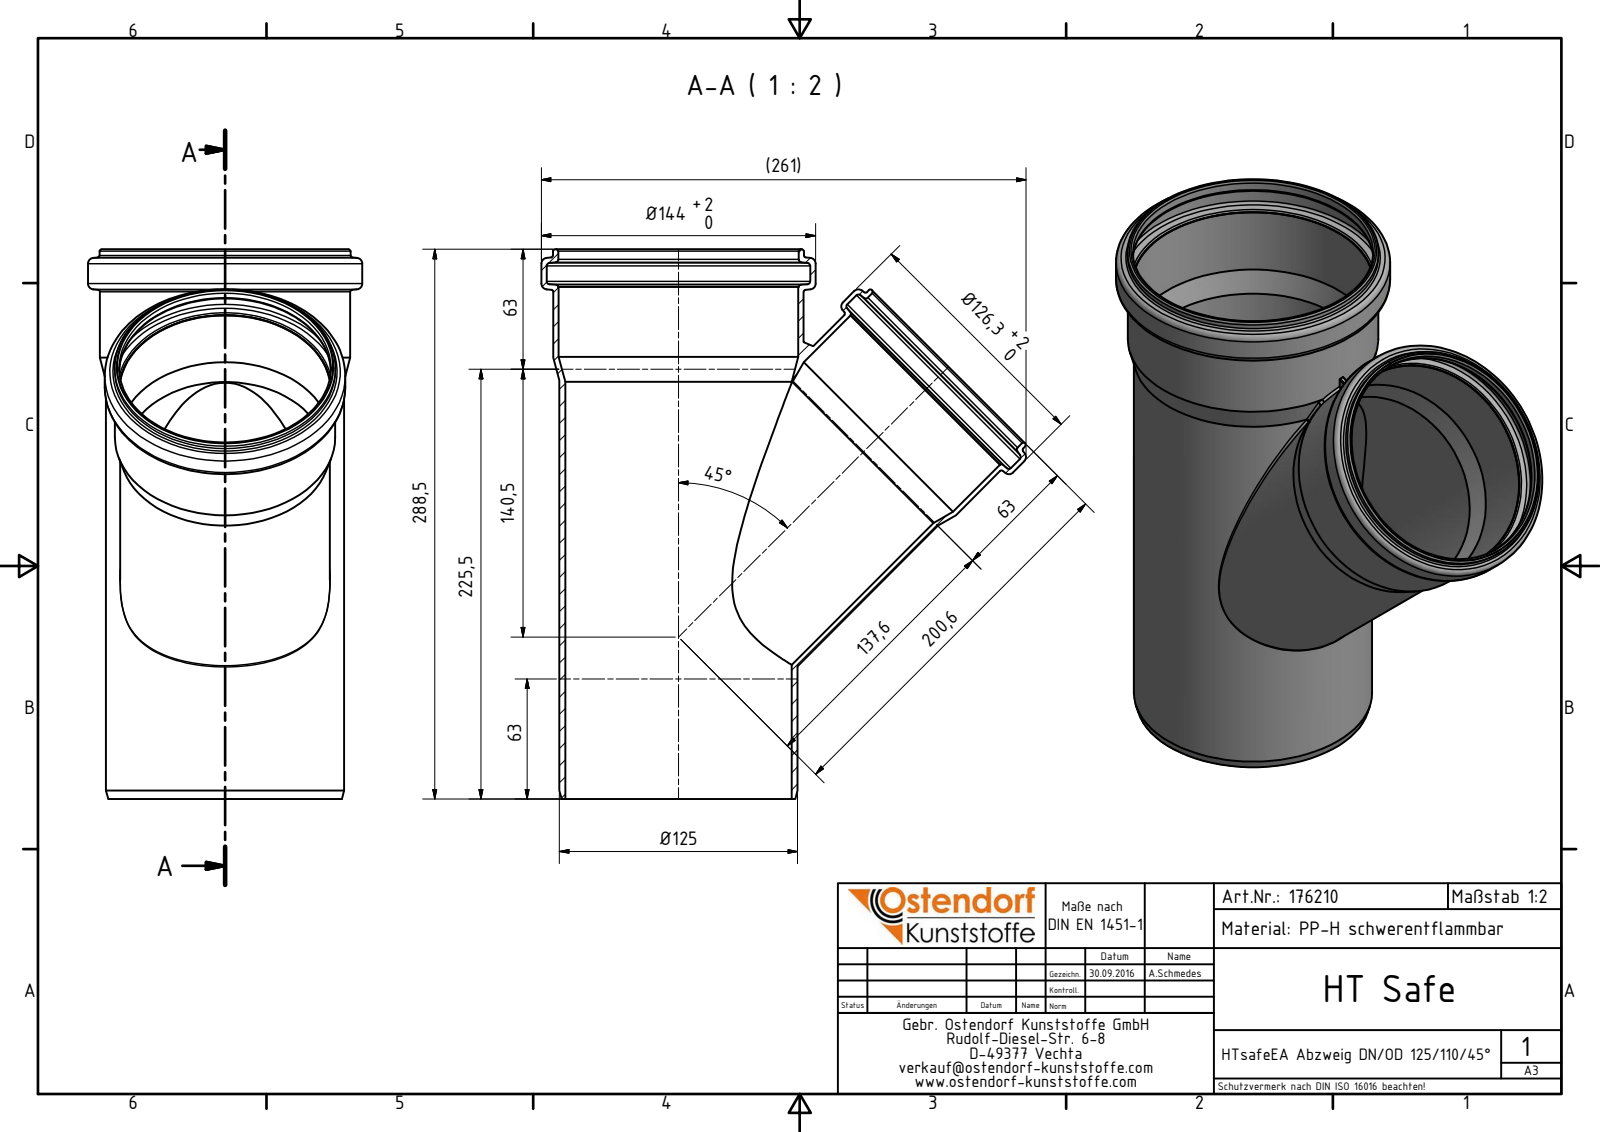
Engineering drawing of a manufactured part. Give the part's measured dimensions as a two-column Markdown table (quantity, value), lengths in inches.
| quantity | value |
| --- | --- |
| part name | 176210 HTsafeEA DN_OD 125_110_45° |
| STEP written by | Autodesk Inventor 2016 (AUTOMOTIVE_DESIGN) |
| units | inches |
| bodies | 1 solid, 70 faces (8 planar, 20 cylindrical, 42 other) |
| overall size | 11.358 × 10.021 × 5.669 |
| volume | 26.43 in³ |
| surface area | 471.7 in² |
| round holes (diameter × count) | 4.378 × 2, 4.122 × 1, 4.366 × 1, 4.681 × 1, 4.783 × 1, 4.957 × 1, 4.969 × 1, 5.449 × 1 |
| round bosses / shafts (diameter × count) | 5.669 × 1, 5.189 × 1, 5.177 × 1, 4.972 × 1, 4.925 × 1, 4.567 × 1, 4.555 × 1, 4.335 × 1 |
| partial cylindrical surfaces (radius × count) | 0.02 × 2 |
| main face-to-face distances | 11.358, 10.58, 0.778, 0.682, 0.11 |
